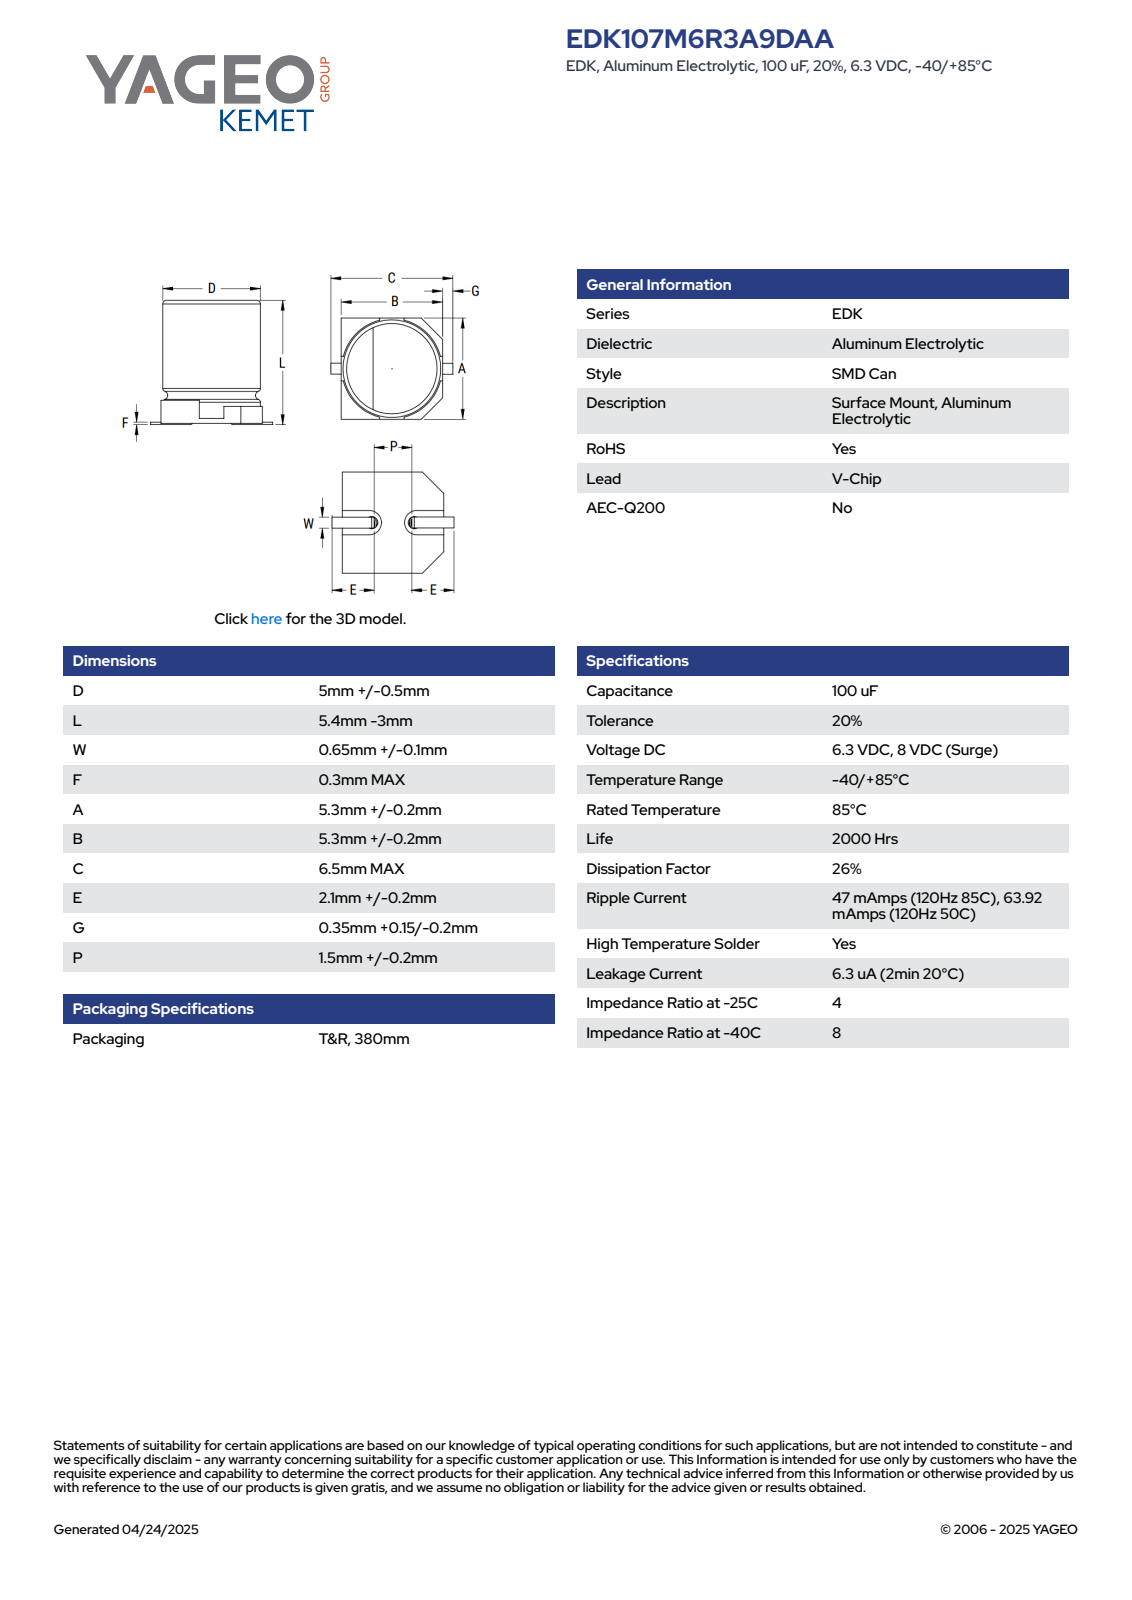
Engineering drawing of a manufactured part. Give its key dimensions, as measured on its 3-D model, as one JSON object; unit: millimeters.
{"part_name": "CAC_S_5X5.4_D5.5L5.65W0.75F0.3A5.5B5.5C6.5E2.4P1.7", "step_written_by": "SolidWorks 2021 (AUTOMOTIVE_DESIGN)", "units": "millimeters", "bodies": {"solids": 5, "faces": 78, "planar": 61, "cylindrical": 11, "other": 6}, "overall_size": [6.3, 5.5, 2.4], "volume_mm3": 49, "surface_area_mm2": 151, "round_bosses_or_shafts": [[5.26, 1]], "partial_cylinders_radius": [[0.2, 2], [2.18, 1], [2.75, 1]], "face_to_face_distances": [2.1, 1.98, 1.5, 0.42, 2.4, 0.9, 0.6, 0.48, 0.4, 5.5]}
